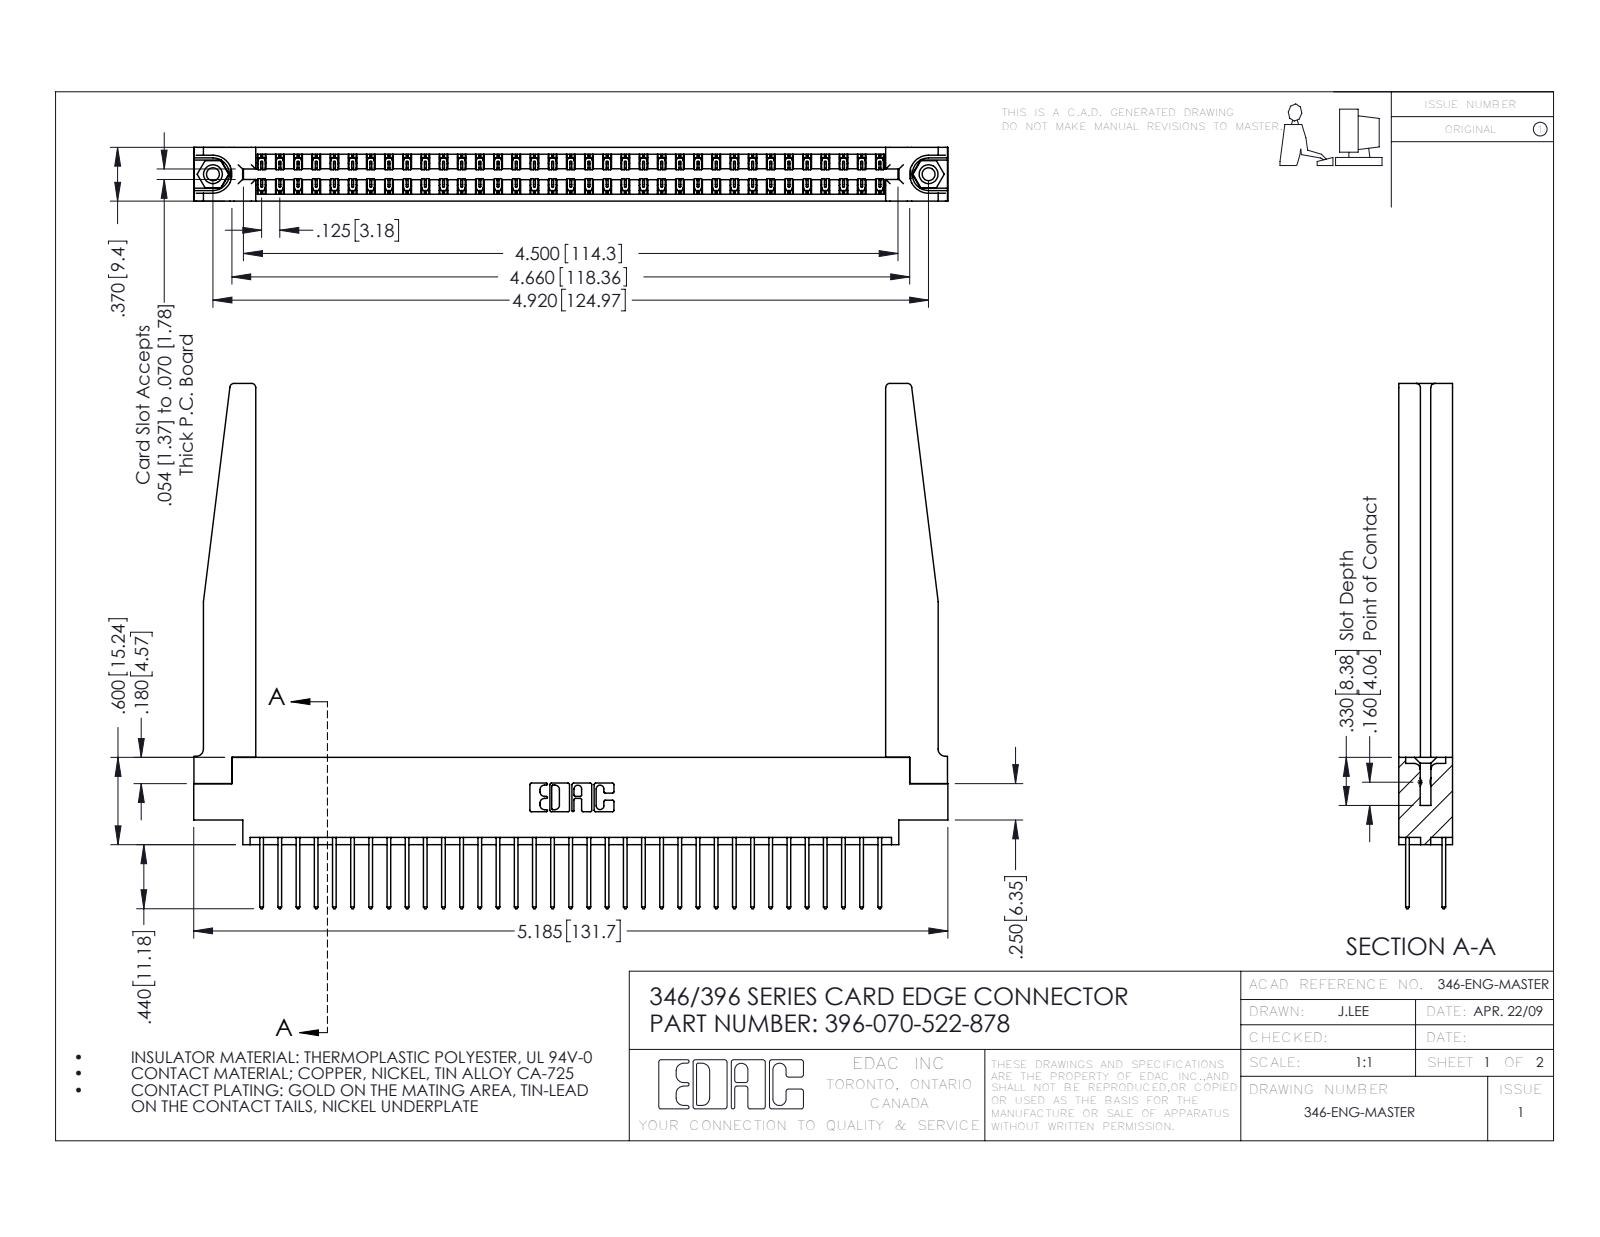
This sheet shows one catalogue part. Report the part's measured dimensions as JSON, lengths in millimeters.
{"part_name": "346-220-078_345-220-078; 345-250-001_345-250-001-102; 396-070-522-878; 345-292-001_345-293-122 (+1 more)", "step_written_by": "SolidWorks 2016 (CONFIG_CONTROL_DESIGN)", "units": "millimeters", "bodies": {"solids": 75, "faces": 4000, "planar": 2672, "cylindrical": 1276, "other": 52}, "overall_size": [131.7, 91.7, 9.4], "volume_mm3": 19710, "surface_area_mm2": 25050, "round_holes": [[2.3, 2], [3.2, 2], [4, 2], [1.6, 1]], "round_bosses_or_shafts": [[3.9, 2]], "partial_cylinders_radius": [[0.2, 105], [0.3, 70], [0.3, 22], [0.8, 8], [0.2, 6], [0.8, 6], [0.7, 3], [0.4, 2]], "face_to_face_distances": [9.4, 1.2, 8.2, 1.8, 6.4, 7.6, 0.6, 3.8, 3.8, 7], "hole_center_spacings": [6.2, 119.7, 125]}
